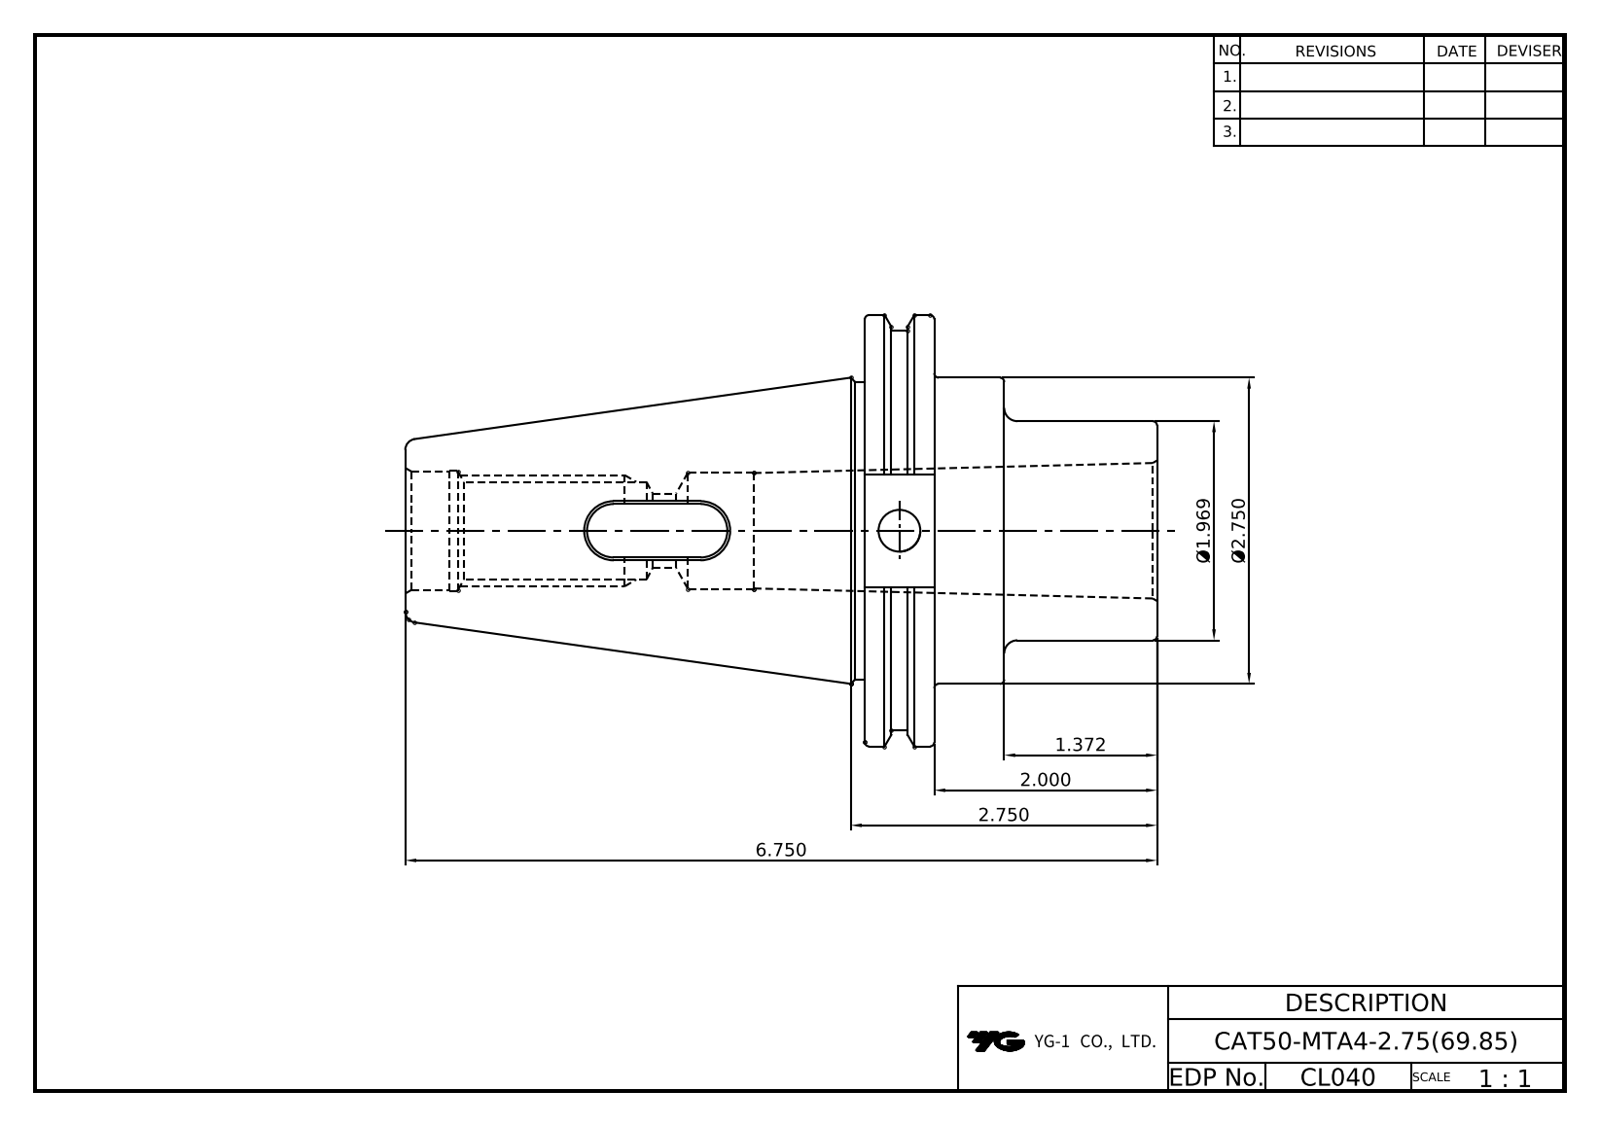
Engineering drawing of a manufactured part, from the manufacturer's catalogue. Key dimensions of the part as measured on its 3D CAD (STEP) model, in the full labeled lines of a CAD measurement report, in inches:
Part name (STEP PRODUCT): LO-CAT50-MTA4-69.85
STEP written by: Autodesk Inventor 2022 (AUTOMOTIVE_DESIGN)
Units: inches
Bodies: 1 solid, 91 faces (35 planar, 19 cylindrical, 37 other)
Overall size (bounding box): 6.75 × 3.875 × 3.728
Volume: 23.81 in³ · Surface area: 91.48 in²
Round holes (diameter × count): ⌀0.375 ×1, ⌀0.865 ×1, ⌀1.031 ×1, ⌀1.043 ×1
Round bosses / shafts (diameter × count): ⌀3.875 ×1, ⌀3.594 ×1, ⌀2.75 ×1, ⌀2.726 ×1, ⌀1.969 ×1
Partial cylindrical surfaces — rounded edges, fillets, slot ends (radius × count): R0.234 ×2, R0.335 ×1
Main face-to-face distances: 0.625, 1.253, 0.628, 2.625, 2, 1.372, 0.469, 0.276, 0.744, 4.125
